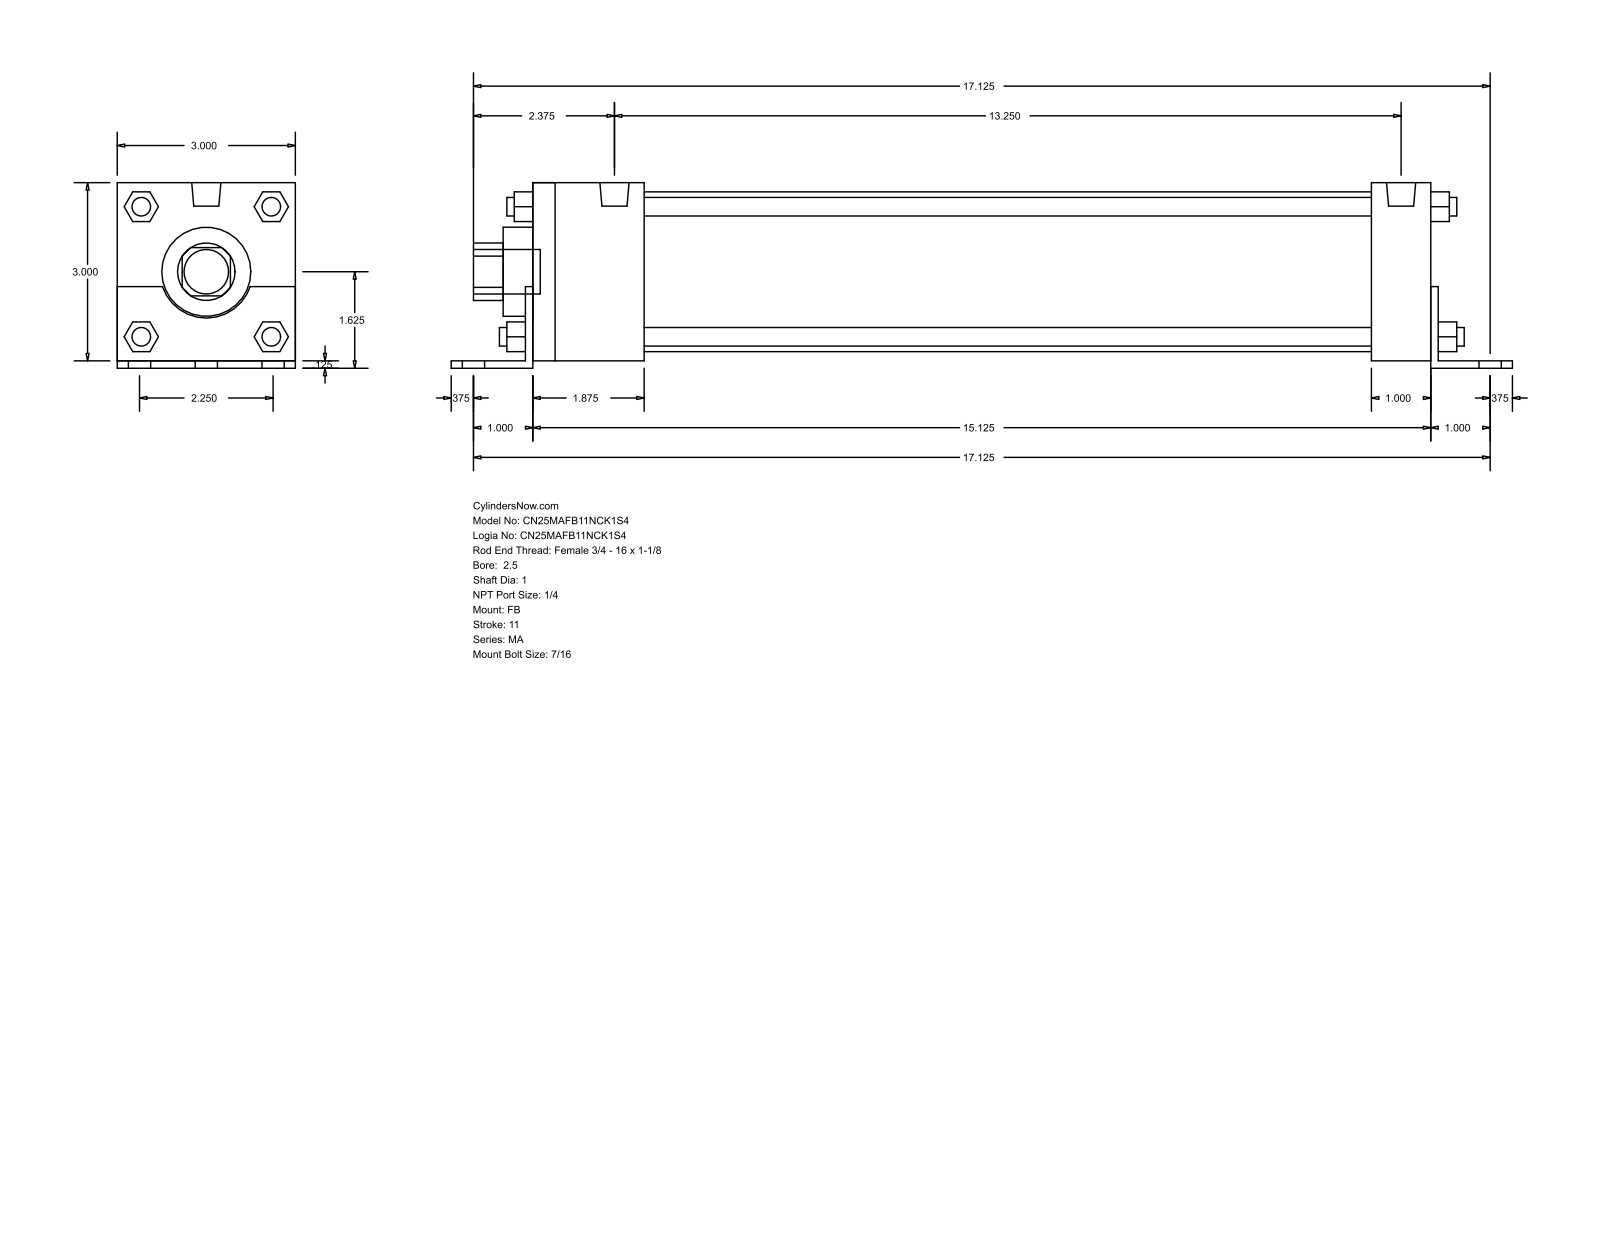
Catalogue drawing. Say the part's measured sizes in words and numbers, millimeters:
The part is named "MA_FB__0250_1". Its 3-D file was written by "GSSL Pune (CONFIG_CONTROL_DESIGN)". It is 0 solids with 140 faces: 105 planar, 35 cylindrical and 0 other. Overall it measures 454.02 by 79.38 by 76.2 millimeters. Round holes: 1 of diameter 25.4, 1 of diameter 38.1, 1 of diameter 68.33. Round bosses or shafts: 8 of diameter 7.94, 6 of diameter 11.11, 2 of diameter 12.49, 1 of diameter 19.05. Partial cylindrical surfaces (rounded edges, fillets, slot ends): 1 of radius 12.29, 1 of radius 19.81. The main face-to-face distances are 76.2, 3.17, 79.37, 384.17, 3.18, 12.7, 387.35, 28.57, 47.63, 336.54.
